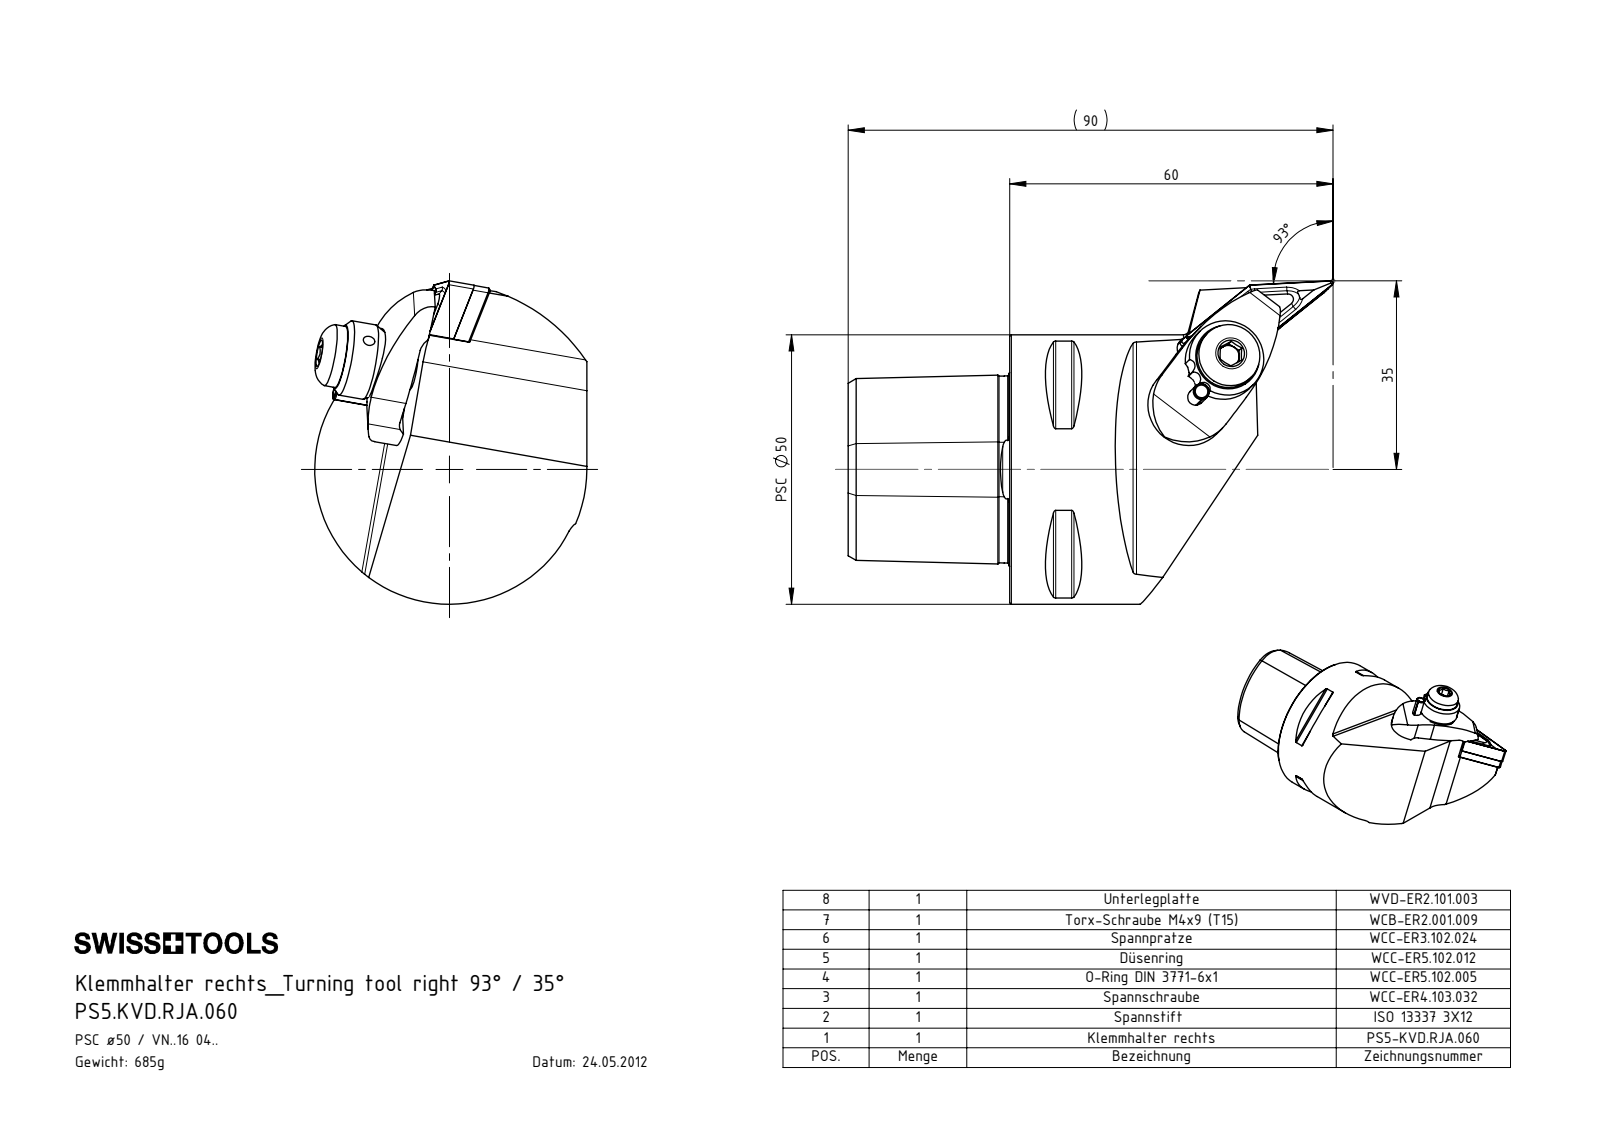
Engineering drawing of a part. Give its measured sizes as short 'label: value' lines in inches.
name: WCC-ER5.102.005_A; PS5.KVD.RJA.060; ISO 13337 - 3 x 12_PreviewCfg; WCC-ER4.103.032_A (+7 more)
written by: SolidWorks 2017 (AUTOMOTIVE_DESIGN)
unit: in
bodies: 11 solids, 433 faces (100 planar, 134 cylindrical, 199 other)
size: 3.543 × 2.362 × 1.988
volume: 5.293 in³; area: 35.95 in²
holes: 3× ⌀0.079, 2× ⌀0.157, 2× ⌀0.197, 2× ⌀0.276, 1× ⌀0.094, 1× ⌀0.118, 1× ⌀0.13, 1× ⌀0.15, 1× ⌀0.165, 1× ⌀0.195, 1× ⌀0.24, 1× ⌀0.244
bosses: 2× ⌀0.157, 2× ⌀0.118, 1× ⌀1.969, 1× ⌀0.551, 1× ⌀0.453, 1× ⌀0.268, 1× ⌀0.244, 1× ⌀0.236
rounds: 10× R0.02, 6× R0.013, 6× R0.023, 4× R0.016, 3× R0.059, 2× R0.079, 2× R0.118, 2× R0.157
face distances: 1.181, 0.301, 0.125, 0.176, 0.051, 0.359, 0.352, 0.227, 0.359, 0.755
hole spacings: 0.563, 0.316, 0.879, 0.556, 0.316, 0.323, 0.323, 0.879
